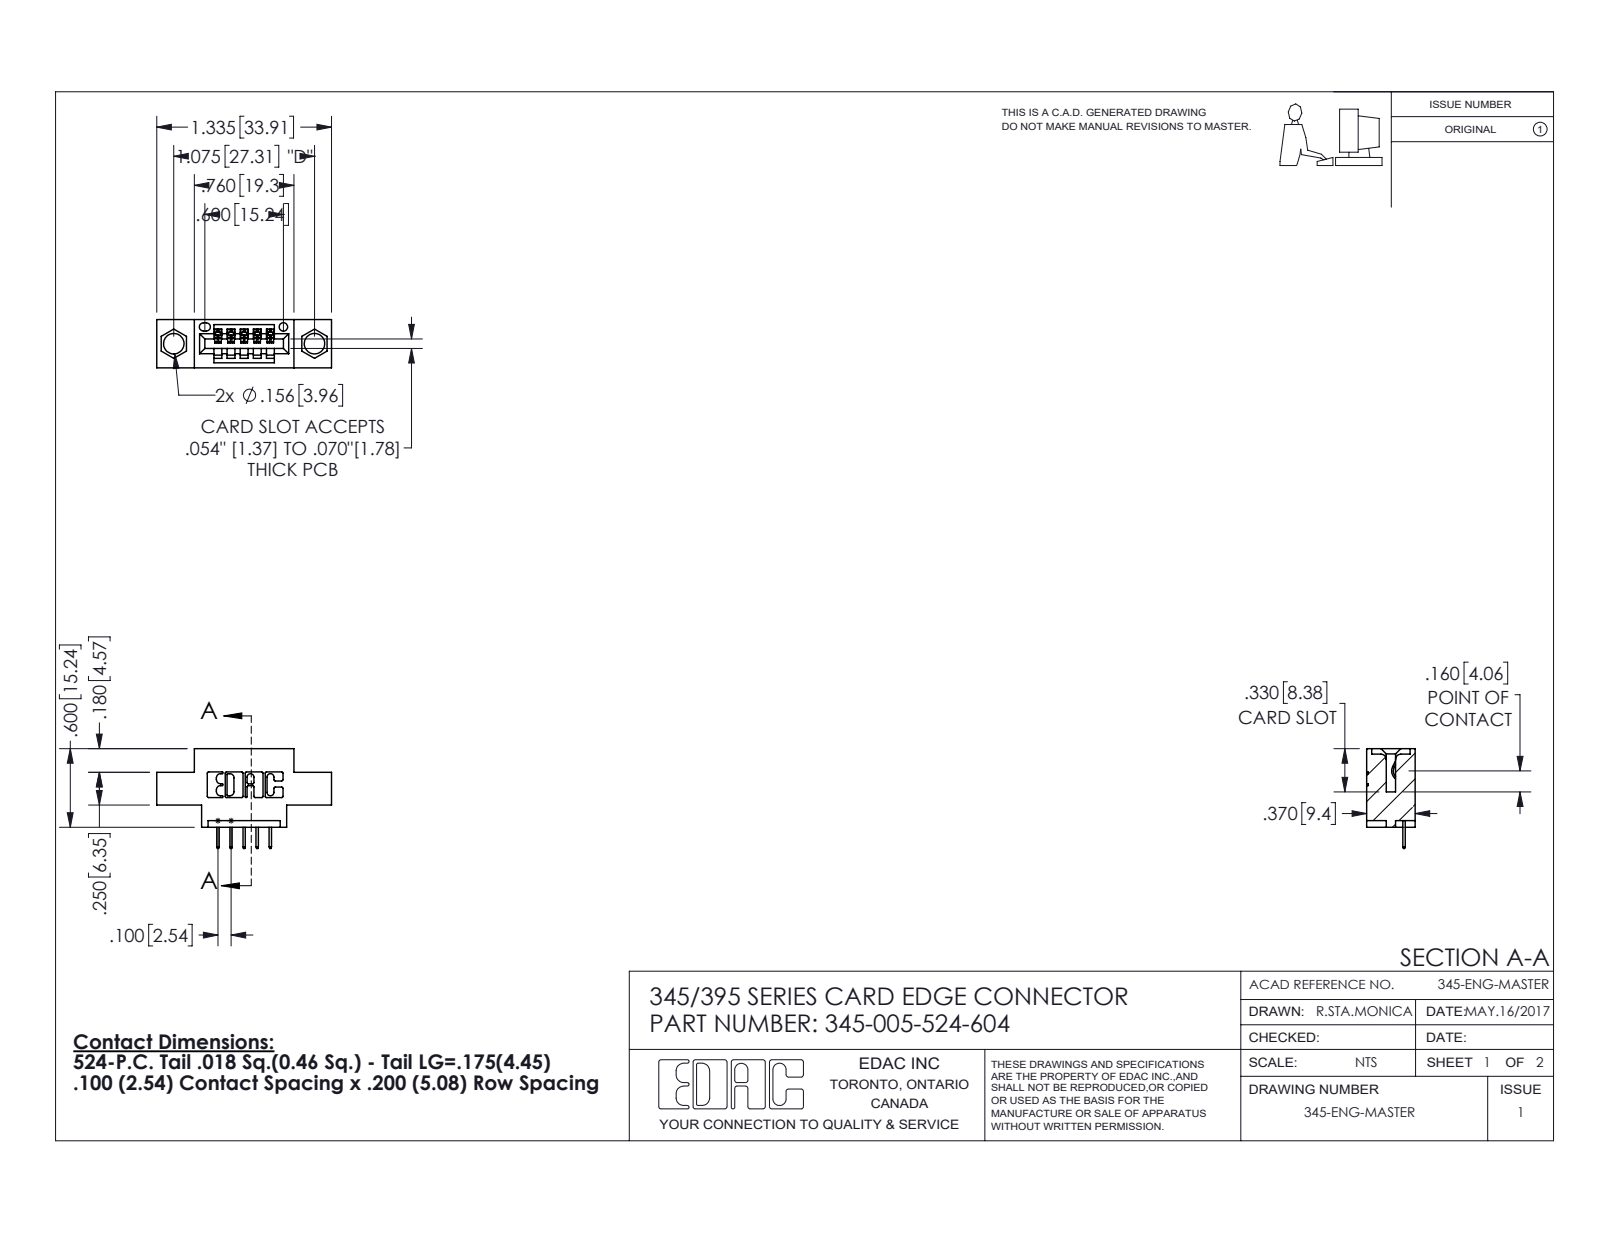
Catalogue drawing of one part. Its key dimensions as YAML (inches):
part_name: "345 Part_0.170 Offset - 0.156 Dia-TH; 345-005-524-604; 345-292-001_345-293-124"
step_written_by: "SolidWorks 2016 (CONFIG_CONTROL_DESIGN)"
units: inches
bodies: {solids: 6, faces: 440, planar: 314, cylindrical: 126, other: 0}
overall_size: [1.335, 0.762, 0.37]
volume: 0.165
surface_area: 4.577
round_holes:
  - {diameter: 0.156, count: 2}
  - {diameter: 0.064, count: 1}
partial_cylinders:
  - {radius: 0.01, count: 22}
  - {radius: 0.006, count: 10}
  - {radius: 0.007, count: 6}
  - {radius: 0.031, count: 6}
  - {radius: 0.026, count: 3}
  - {radius: 0.031, count: 2}
  - {radius: 0.04, count: 2}
  - {radius: 0.014, count: 1}
face_to_face_distances: [0.37, 0.2, 0.1, 0.072, 0.298, 0.25, 0.025, 0.06, 0.55, 0.15]
hole_center_spacings: [0.27, 0.847, 1.075]
